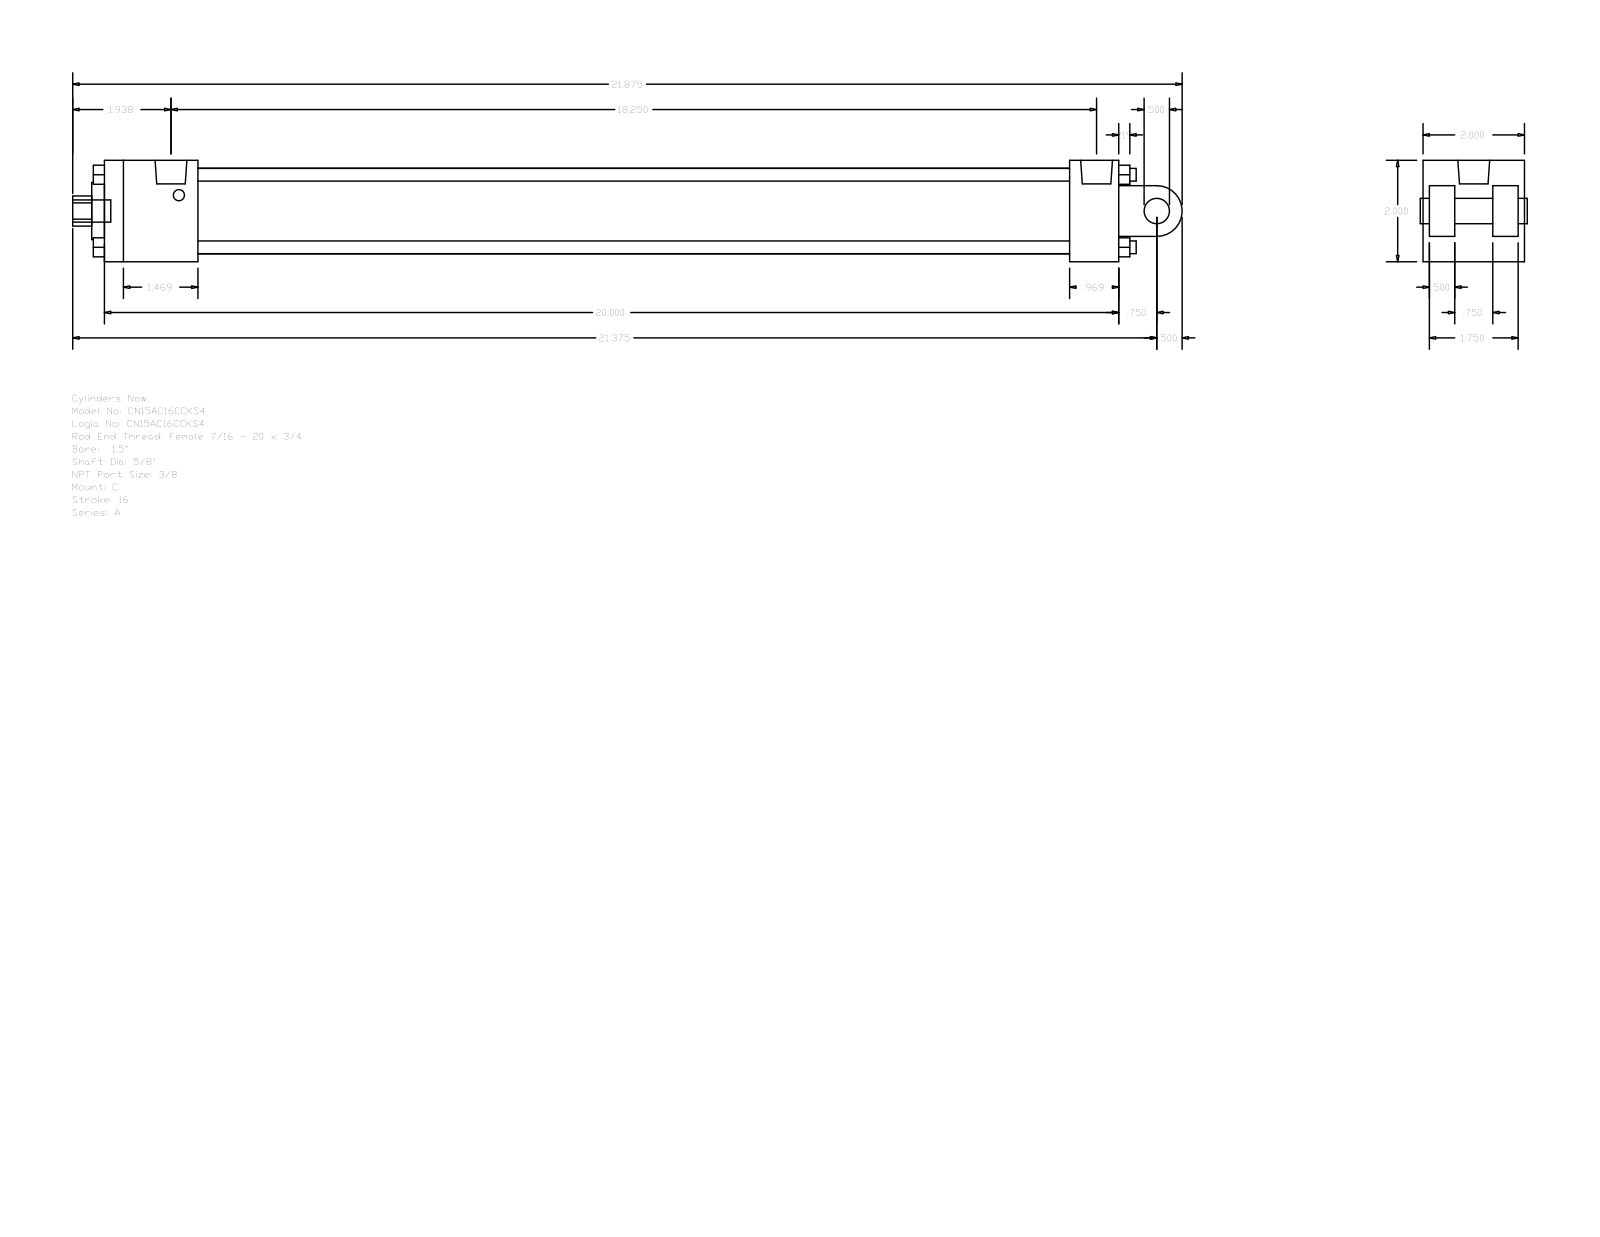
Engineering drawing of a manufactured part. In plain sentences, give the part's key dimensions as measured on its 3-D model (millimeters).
The part is named "A_C__0150_0.625". Its 3-D file was written by "GSSL Pune (CONFIG_CONTROL_DESIGN)". It is 0 solids with 135 faces: 102 planar, 33 cylindrical and 0 other. Overall it measures 555.62 by 50.8 by 50.8 millimeters. Round holes: 2 of diameter 5.56, 1 of diameter 15.88, 1 of diameter 15.93, 1 of diameter 28.57, 1 of diameter 42.93. Round bosses or shafts: 4 of diameter 6.35, 2 of diameter 5.56, 1 of diameter 15.93, 1 of diameter 12.7, 1 of diameter 11.11. Partial cylindrical surfaces (rounded edges, fillets, slot ends): 1 of radius 7.54, 1 of radius 12.7. The main face-to-face distances are 50.8, 12.7, 508, 3.17, 47.63, 15.87, 34.93, 31.76, 483.39, 24.61. The hole center spacings are 3.97.
